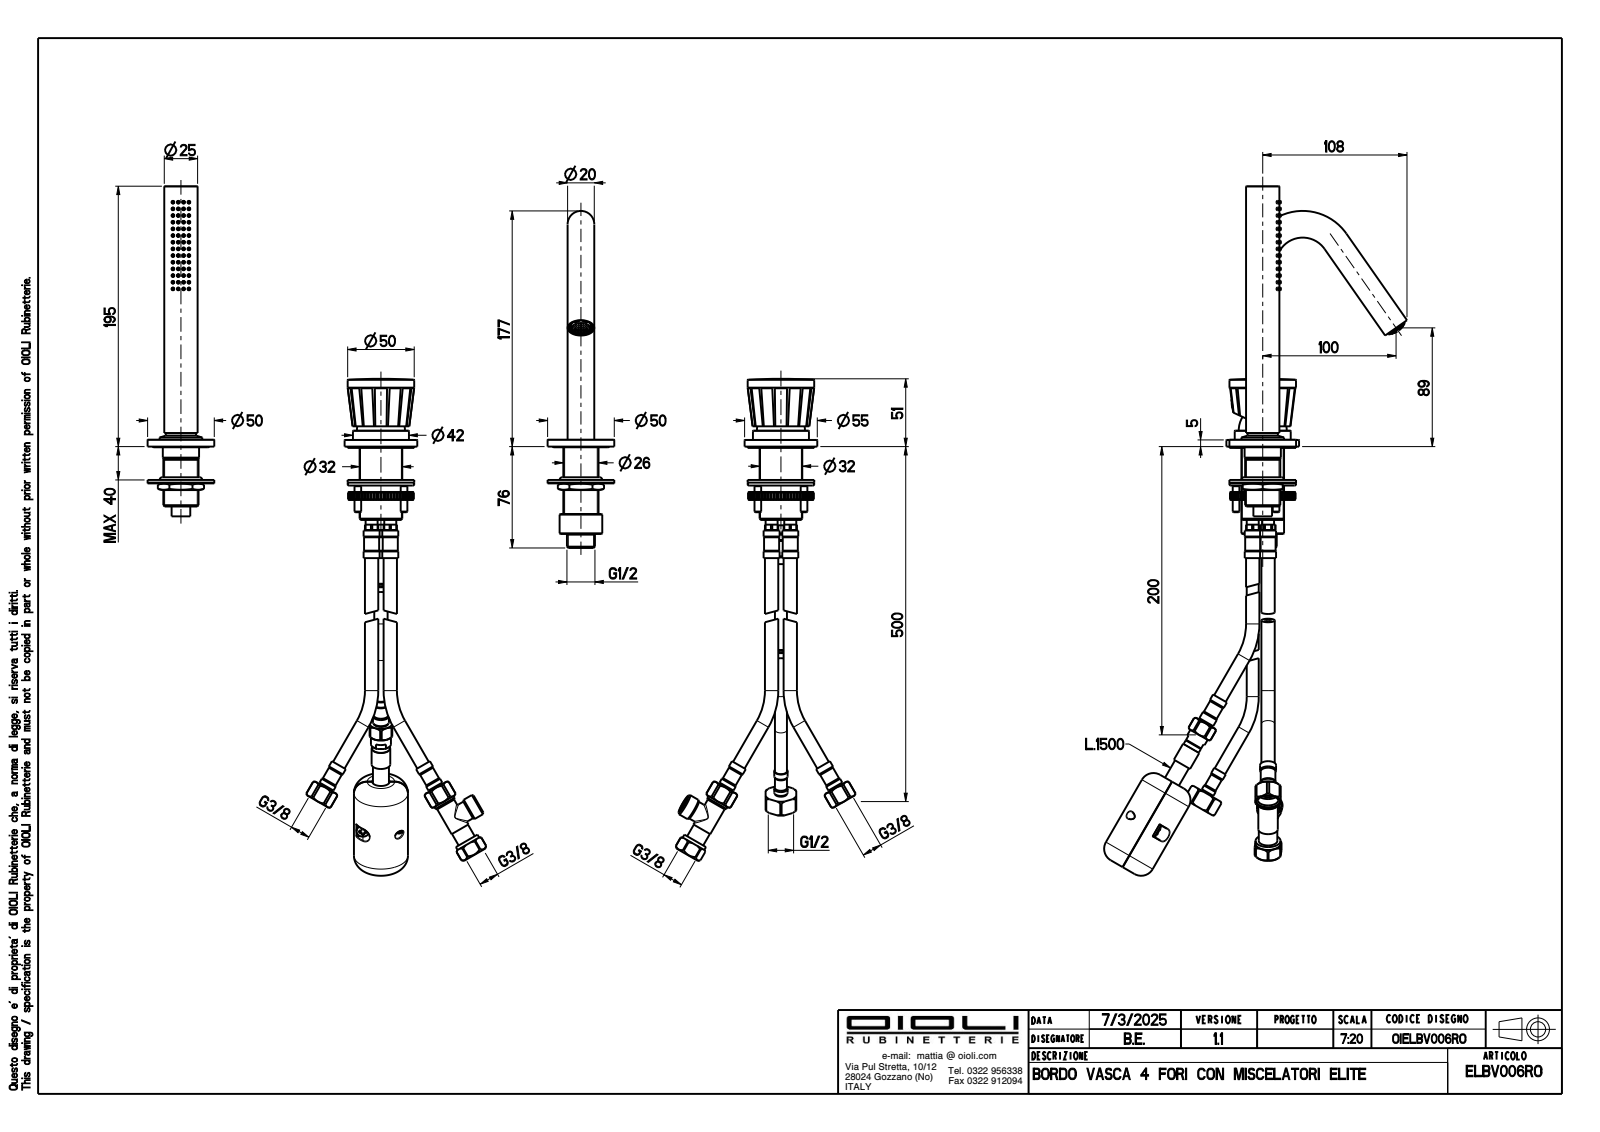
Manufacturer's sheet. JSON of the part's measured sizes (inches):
{"part_name": "OIBR00419; OIBR00148; OIBR00455; OIBR00308 (+8 more)", "step_written_by": "CREO PARAMETRIC BY PTC INC, 2024493 (CONFIG_CONTROL_DESIGN)", "units": "inches", "bodies": {"solids": 17, "faces": 1208, "planar": 236, "cylindrical": 535, "other": 437}, "overall_size": [19.774, 9.85, 5.332], "volume_in3": 17.43, "surface_area_in2": 264.5, "round_holes": [[0.024, 81], [0.276, 12], [0.354, 7], [0.128, 4], [0.157, 2], [0.165, 2], [0.209, 2], [0.256, 2], [0.394, 2], [0.669, 2], [1.031, 2], [1.181, 2]], "round_bosses_or_shafts": [[0.315, 6], [1.26, 3], [2.146, 2], [1.969, 2], [1.965, 2], [1.654, 2], [1.437, 2], [1.299, 2]], "partial_cylinders_radius": [[0.004, 20], [0.394, 1], [0.531, 1]], "face_to_face_distances": [0.205, 0.197, 0.079, 0.118, 0.126, 1.878, 1.799, 1.681, 1.673, 0.276], "hole_center_spacings": [0.196, 0.13, 0.065, 0.195, 11.811, 0.051, 0.235, 0.172]}
